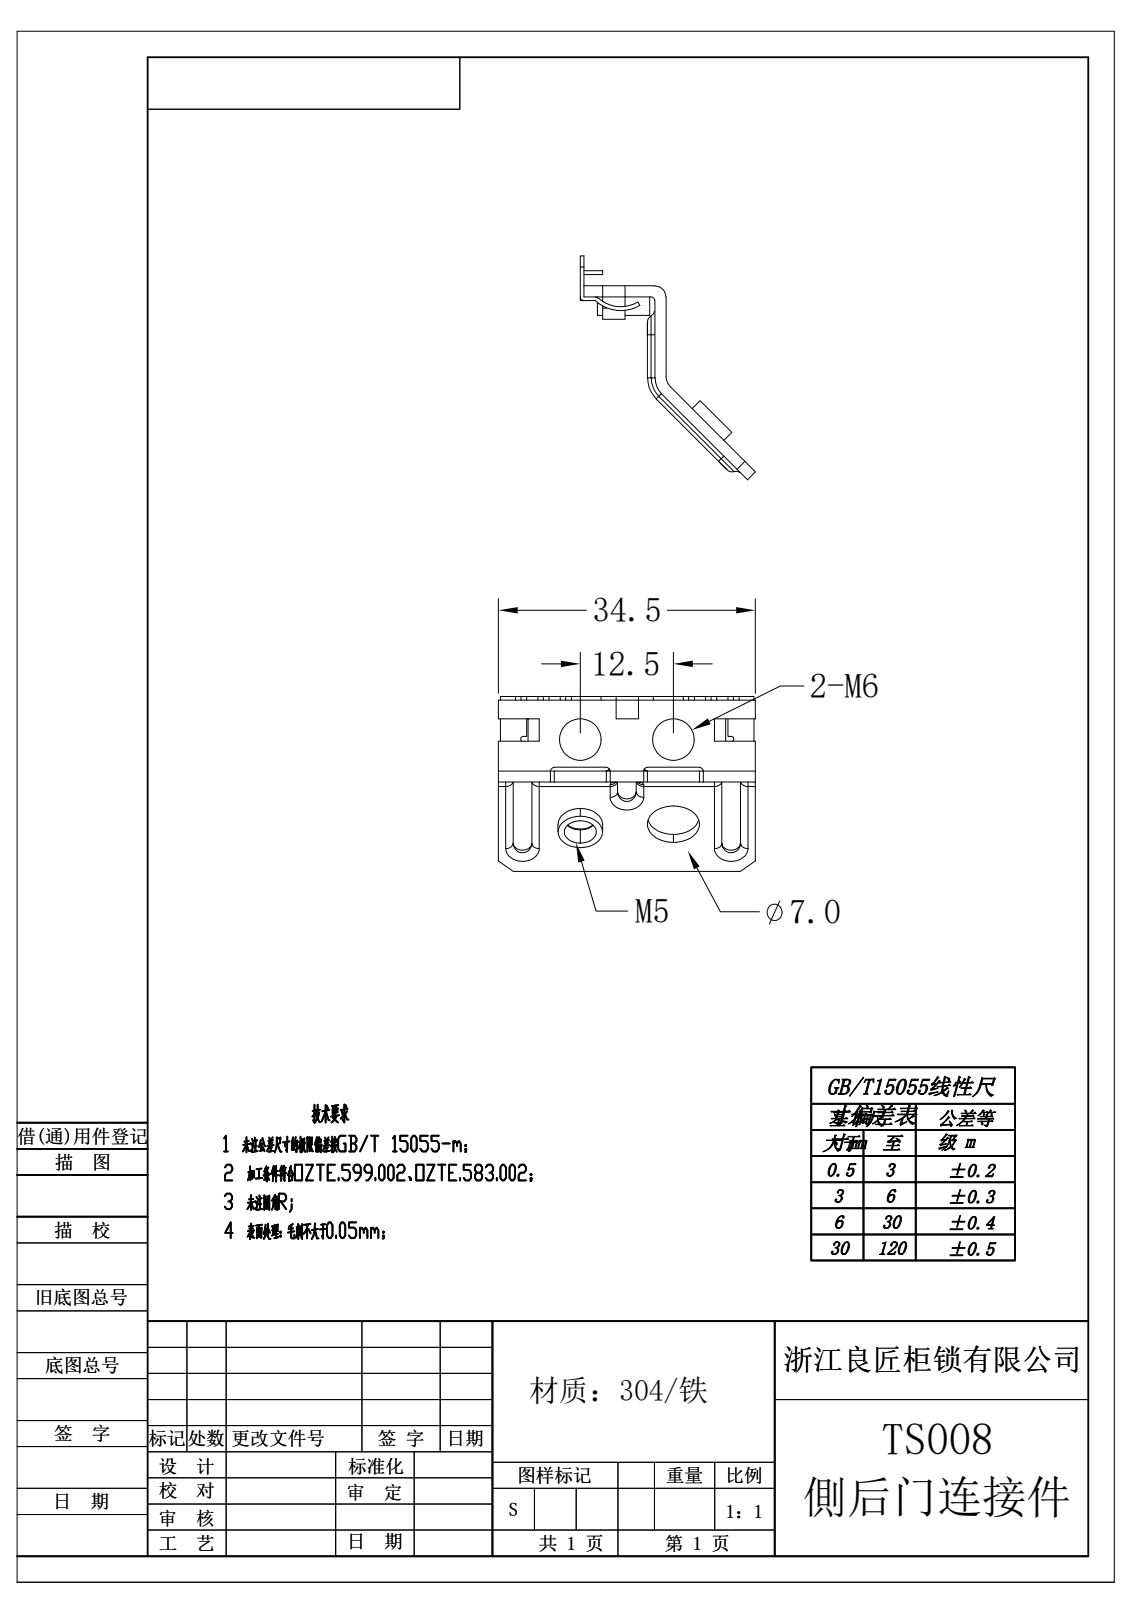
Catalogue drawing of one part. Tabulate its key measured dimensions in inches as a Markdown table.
| quantity | value |
| --- | --- |
| part name | TS008_ASM; TS008; TS008-1 |
| STEP written by | Rhino 8.5 (CONFIG_CONTROL_DESIGN) |
| units | inches |
| bodies | 2 solids, 245 faces (105 planar, 94 cylindrical, 46 other) |
| overall size | 1.358 × 1.183 × 0.925 |
| volume | 0.128 in³ |
| surface area | 5.744 in² |
| round holes (diameter × count) | 0.22 × 2, 0.169 × 1, 0.276 × 1 |
| round bosses / shafts (diameter × count) | 0.276 × 2, 0.236 × 1 |
| partial cylindrical surfaces (radius × count) | 0.039 × 32, 0.02 × 13, 0.049 × 6, 0.059 × 5, 0.118 × 2, 0.079 × 1, 0.157 × 1, 0.177 × 1 |
| main face-to-face distances | 0.059, 0.02, 0.039, 0.098, 0.374, 0.433, 0.118, 0.394, 0.453, 0.157 |
| hole center spacings | 0.492 |
